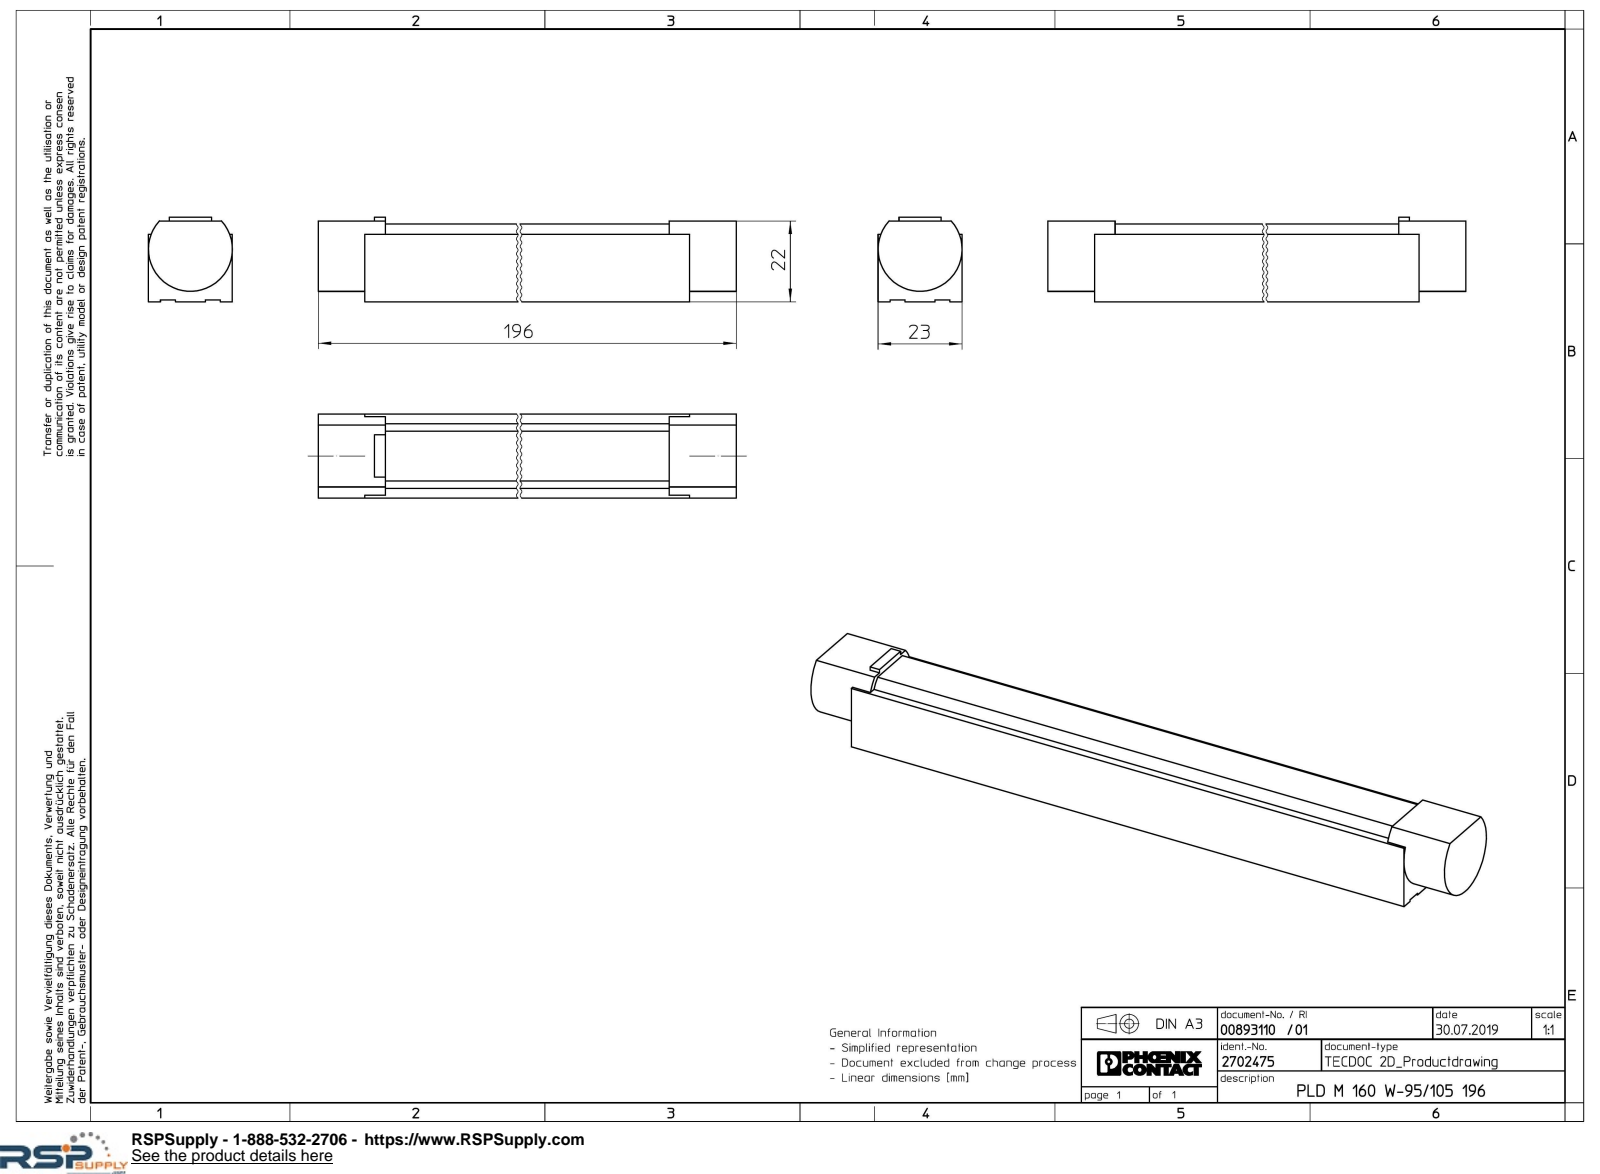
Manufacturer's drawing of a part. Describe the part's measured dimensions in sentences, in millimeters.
The part is named "PLD_M_160_W_95_105_196-select". Its 3-D file was written by "Creo Elements/Direct Modeling 20.1A 29-Sep-2018 (C) Parametric Technology GmbH (AUTOMOTIVE_DESIGN)". It is 1 solid with 40 faces: 32 planar, 8 cylindrical and 0 other. Overall it measures 196 by 22.6 by 22.5 millimeters. Its volume is 85 110 cubic millimeters and its surface area 17 525 square millimeters. Round holes: 2 of diameter 4.4. Partial cylindrical surfaces (rounded edges, fillets, slot ends): 1 of radius 9.5, 1 of radius 11.25. The main face-to-face distances are 22.5, 20.8, 0.5, 20.3, 18, 17.5, 2.8, 21.6, 21.1, 3.6. The hole center spacings are 150.
